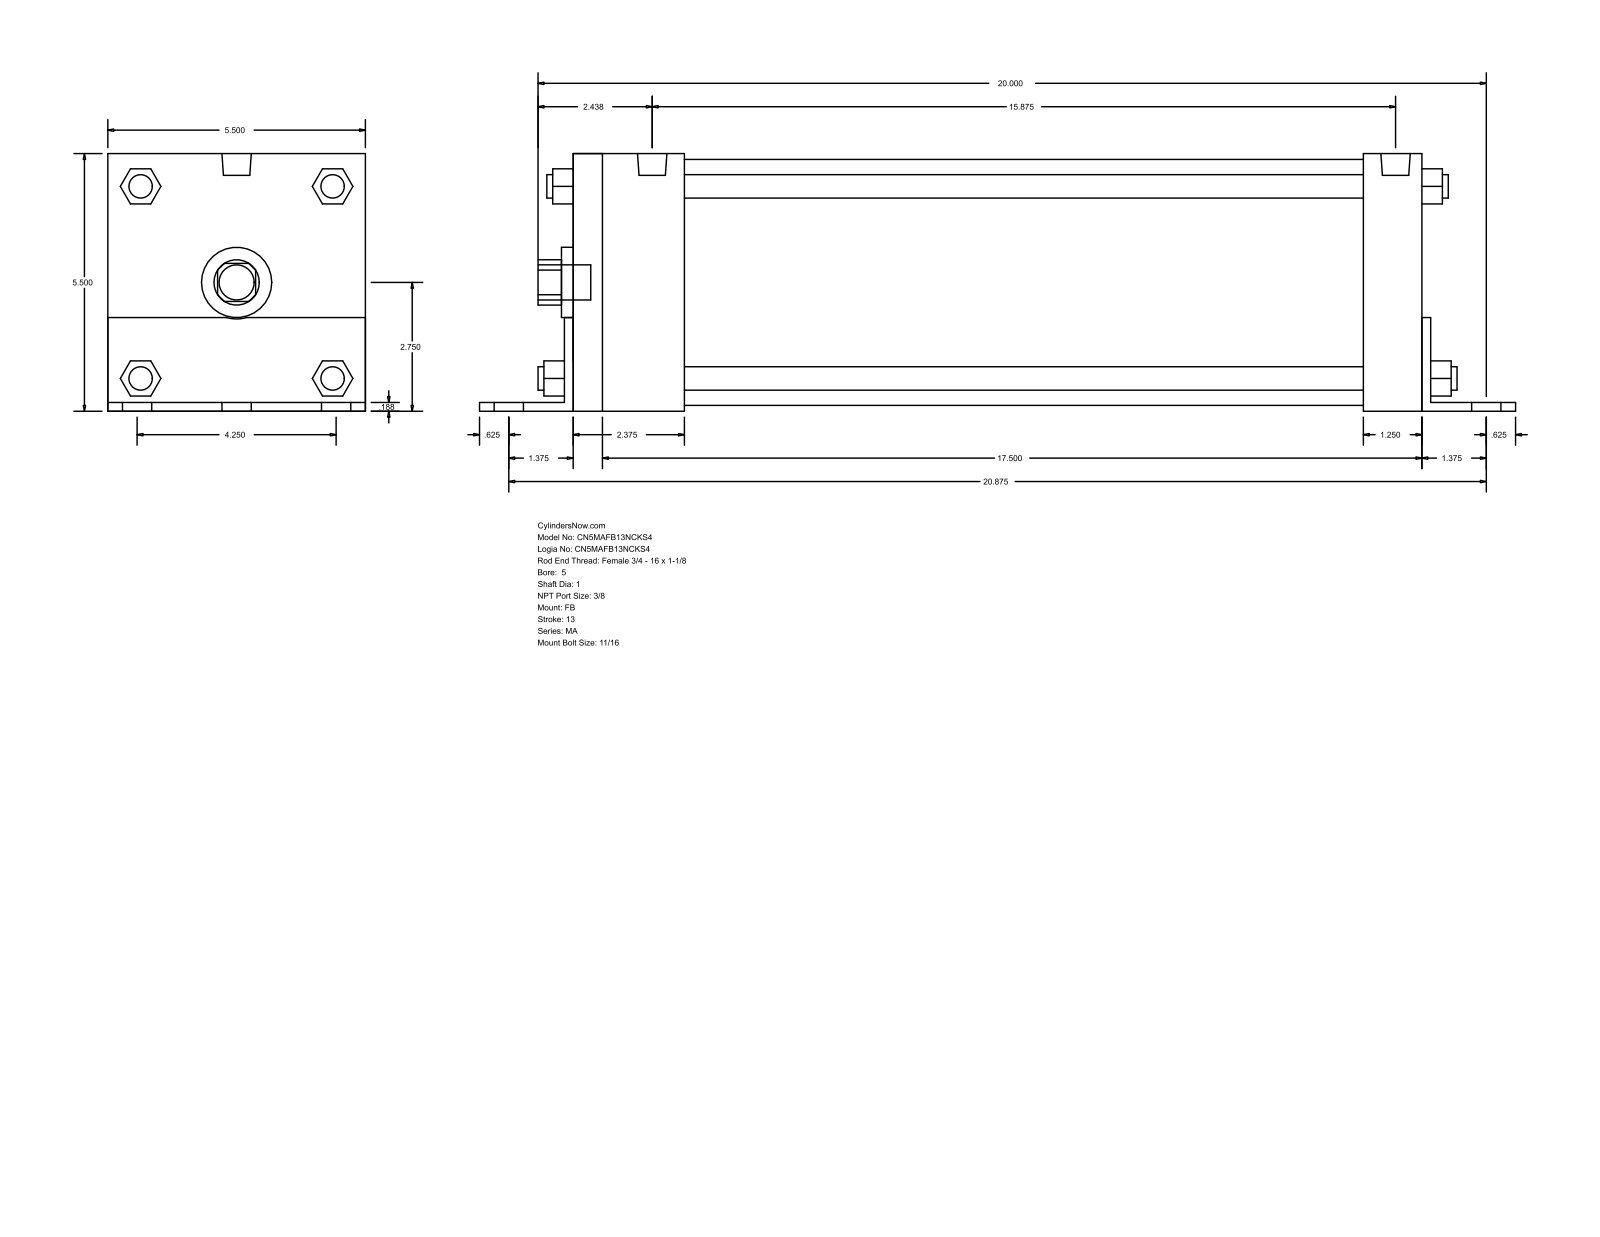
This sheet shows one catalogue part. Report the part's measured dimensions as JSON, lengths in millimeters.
{"part_name": "MA_FB__0500_1", "step_written_by": "GSSL Pune (CONFIG_CONTROL_DESIGN)", "units": "millimeters", "bodies": {"solids": 0, "faces": 140, "planar": 105, "cylindrical": 35, "other": 0}, "overall_size": [561.98, 139.75, 139.7], "round_holes": [[25.4, 1], [38.1, 1], [133.35, 1]], "round_bosses_or_shafts": [[17.46, 6], [12.7, 4], [11.11, 4], [15.93, 2], [19.05, 1]], "partial_cylinders_radius": [[12.29, 1], [19.81, 1]], "face_to_face_distances": [139.7, 4.76, 139.75, 465.14, 4.71, 134.99, 460.38, 469.9, 31.75, 36.51]}
